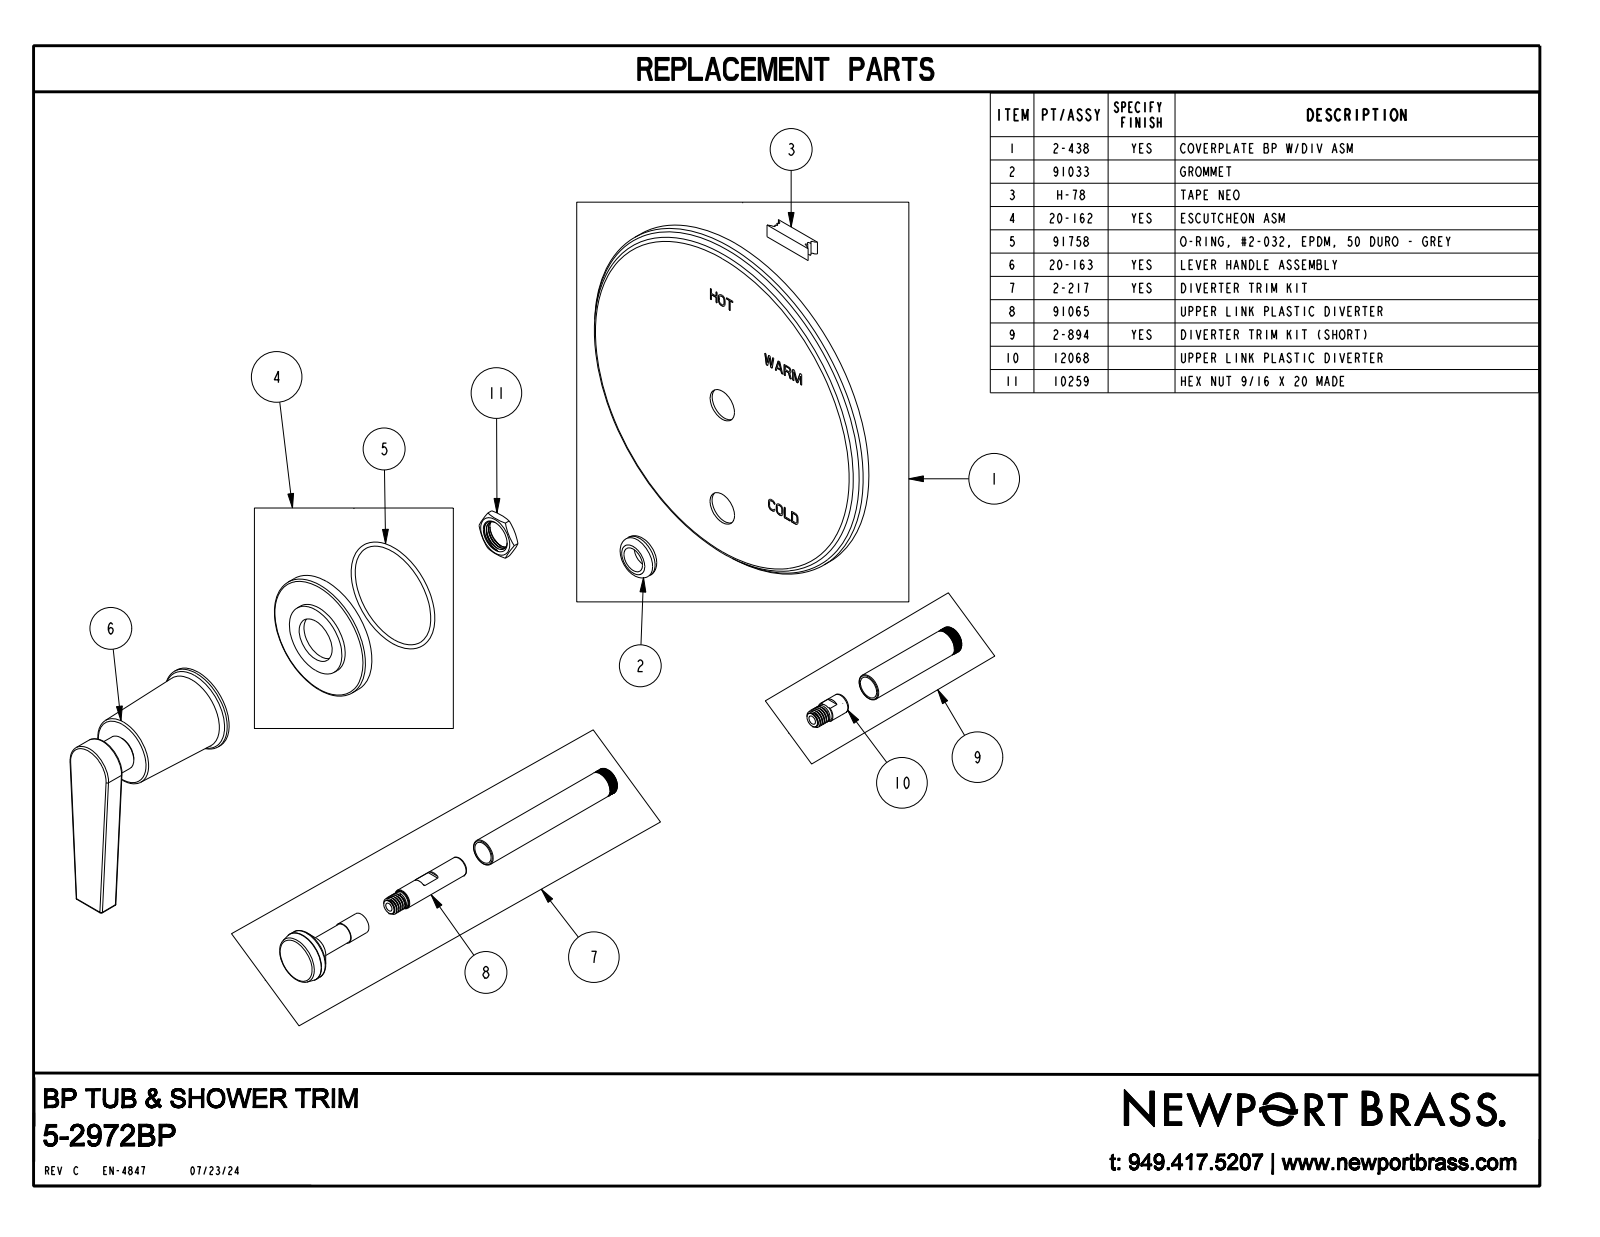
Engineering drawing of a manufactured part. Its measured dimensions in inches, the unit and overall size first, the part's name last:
Units: inches
Overall size (bounding box): 6.5 × 6.5 × 3.183
Round holes (diameter × count): ⌀0.463 ×1
Round bosses / shafts (diameter × count): ⌀6.5 ×1, ⌀2.2 ×1, ⌀1.5 ×1, ⌀1.275 ×1, ⌀0.9 ×1, ⌀0.625 ×1, ⌀0.525 ×1, ⌀0.472 ×1
Partial cylindrical surfaces — rounded edges, fillets, slot ends (radius × count): R0.03 ×8, R0.46 ×1
Main face-to-face distances: 0.313, 0.187, 0.5, 3.183, 2.87, 2.683, 2.808, 2.495, 2.308, 0.375
Volume: 14.74 in³ · Surface area: 91.51 in²
Bodies: 1 solid, 345 faces (276 planar, 31 cylindrical, 38 other)
Part name (STEP PRODUCT): 5-2972BP
STEP written by: CREO PARAMETRIC BY PTC INC, 2018400 (CONFIG_CONTROL_DESIGN)
